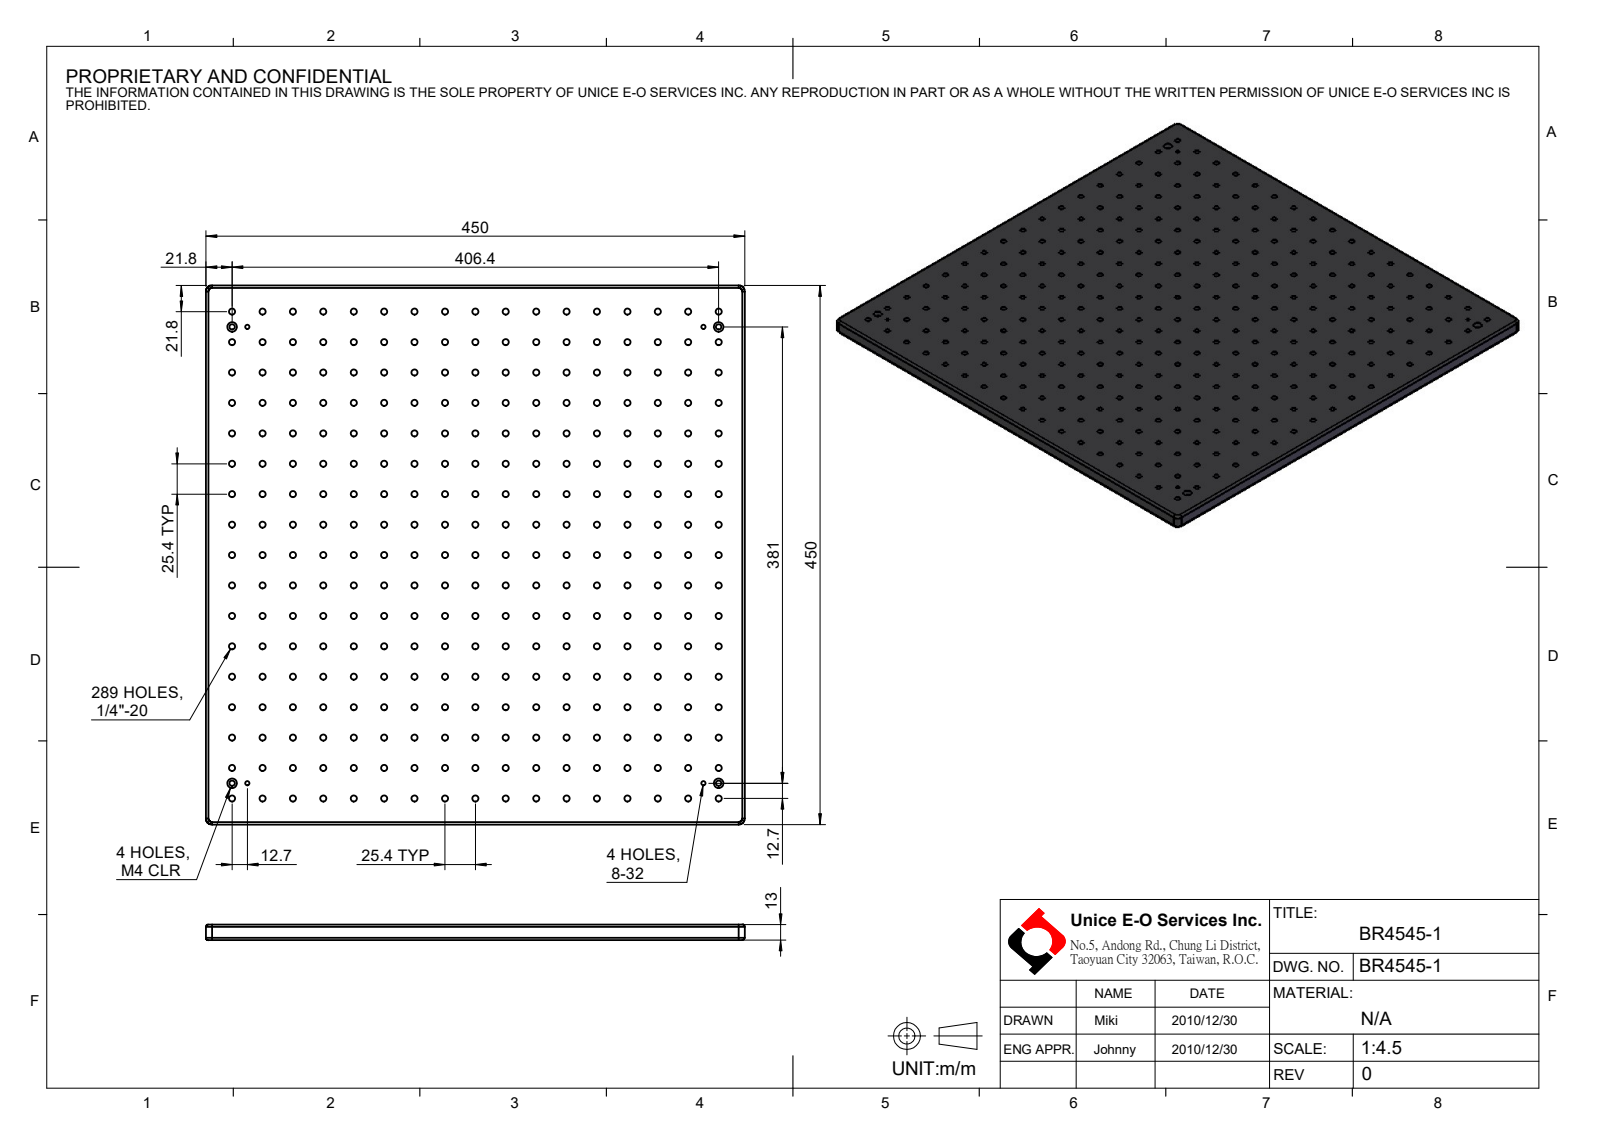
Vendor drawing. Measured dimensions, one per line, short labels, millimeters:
name: BR4545-1
written by: SolidWorks 2016 (CONFIG_CONTROL_DESIGN)
unit: mm
bodies: 1 solid, 632 faces (10 planar, 614 cylindrical, 8 other)
size: 450 × 450 × 13
volume: 2 550 000 mm³; area: 474 883 mm²
holes: 289× ⌀5.11, 4× ⌀3.45, 4× ⌀4.5, 4× ⌀8
rounds: 8× R2, 4× R5
face distances: 13, 450, 8.6, 4.4
hole spacings: 25.4, 56.8, 35.92, 50.8, 80.32, 104.73, 76.2, 71.84
